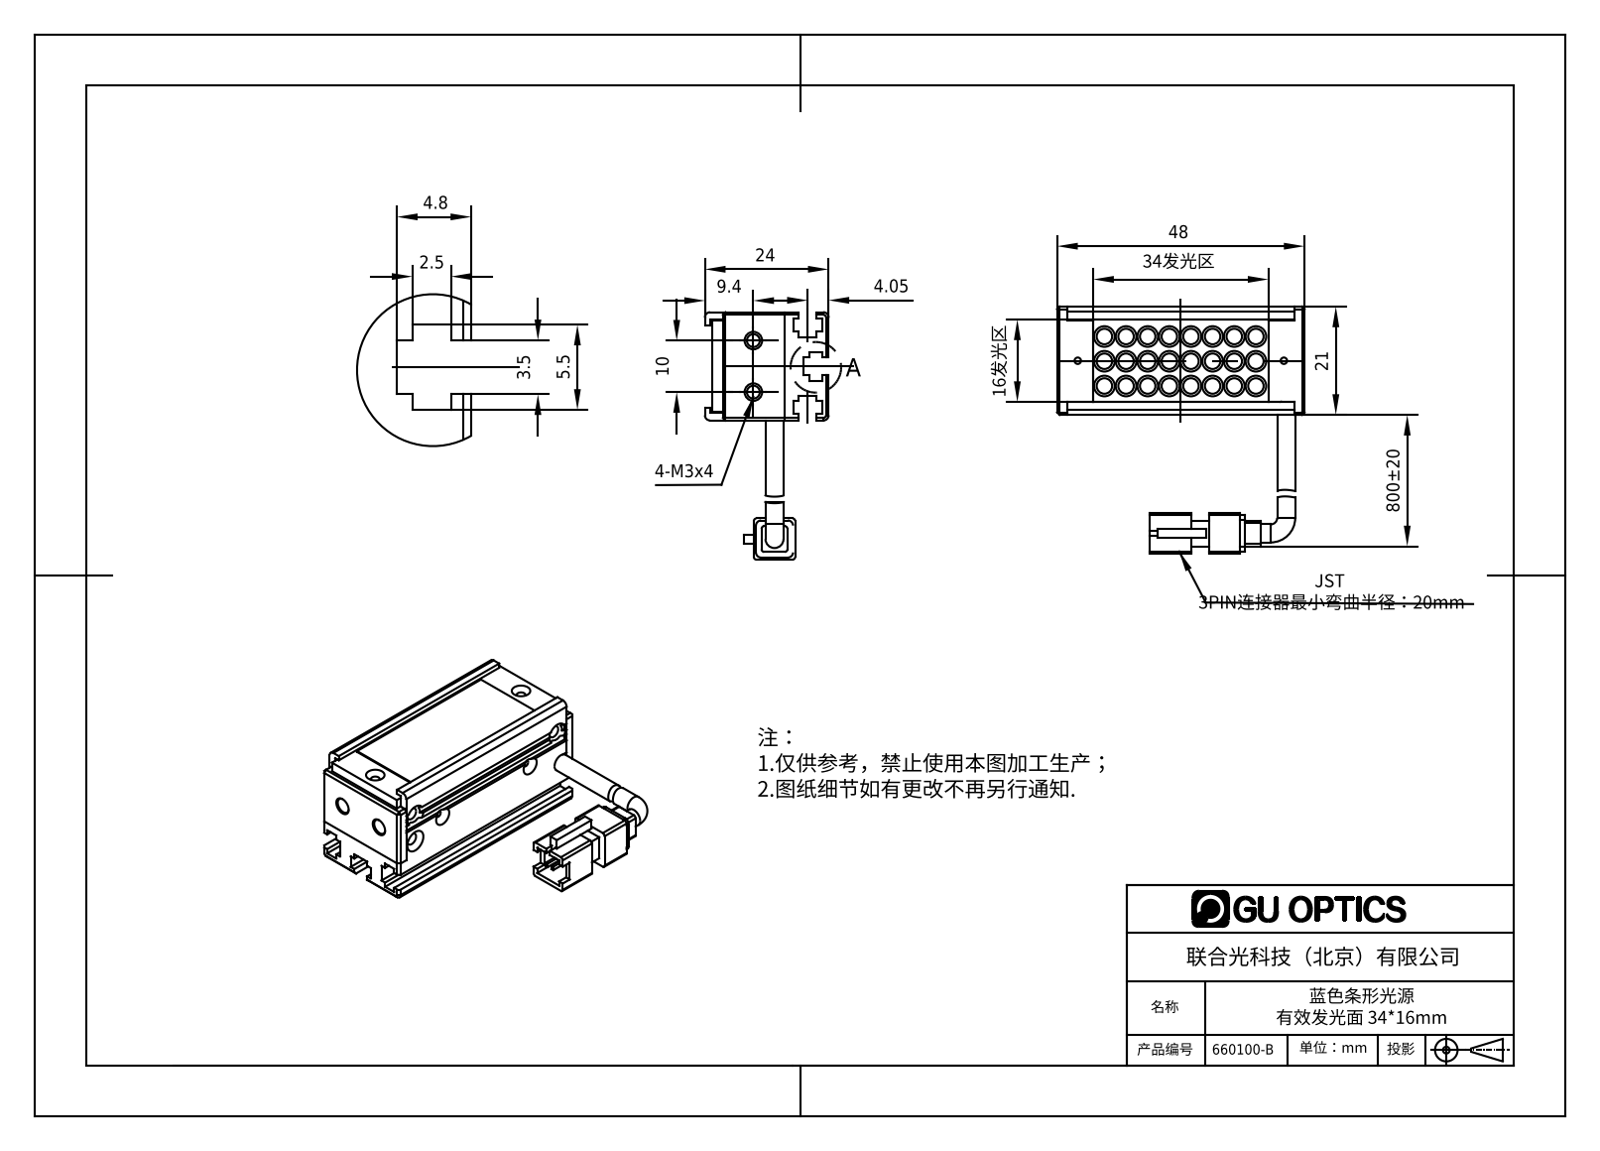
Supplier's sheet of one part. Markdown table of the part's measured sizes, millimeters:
| quantity | value |
| --- | --- |
| part name | 660100-B |
| STEP written by | SolidWorks 2016 (AUTOMOTIVE_DESIGN) |
| units | millimeters |
| bodies | 6 solids, 878 faces (536 planar, 193 cylindrical, 149 other) |
| overall size | 48 × 48 × 24 |
| volume | 15 504 mm³ |
| surface area | 16 054 mm² |
| round holes (diameter × count) | 1.25 × 4, 1.6 × 4, 2.4 × 4, 1.7 × 2, 2.5 × 2, 3 × 2, 2 × 1 |
| round bosses / shafts (diameter × count) | 4 × 24, 3 × 24, 3.5 × 2 |
| partial cylindrical surfaces (radius × count) | 1 × 12, 0.5 × 8, 0.99 × 4, 1.65 × 1 |
| main face-to-face distances | 1, 2.5, 2, 18.5, 20.5, 1.3, 3.5, 12, 8.5, 15.7 |
| hole center spacings | 6, 7.79, 8.45, 31.57, 31.74, 39, 39.46, 10 |
